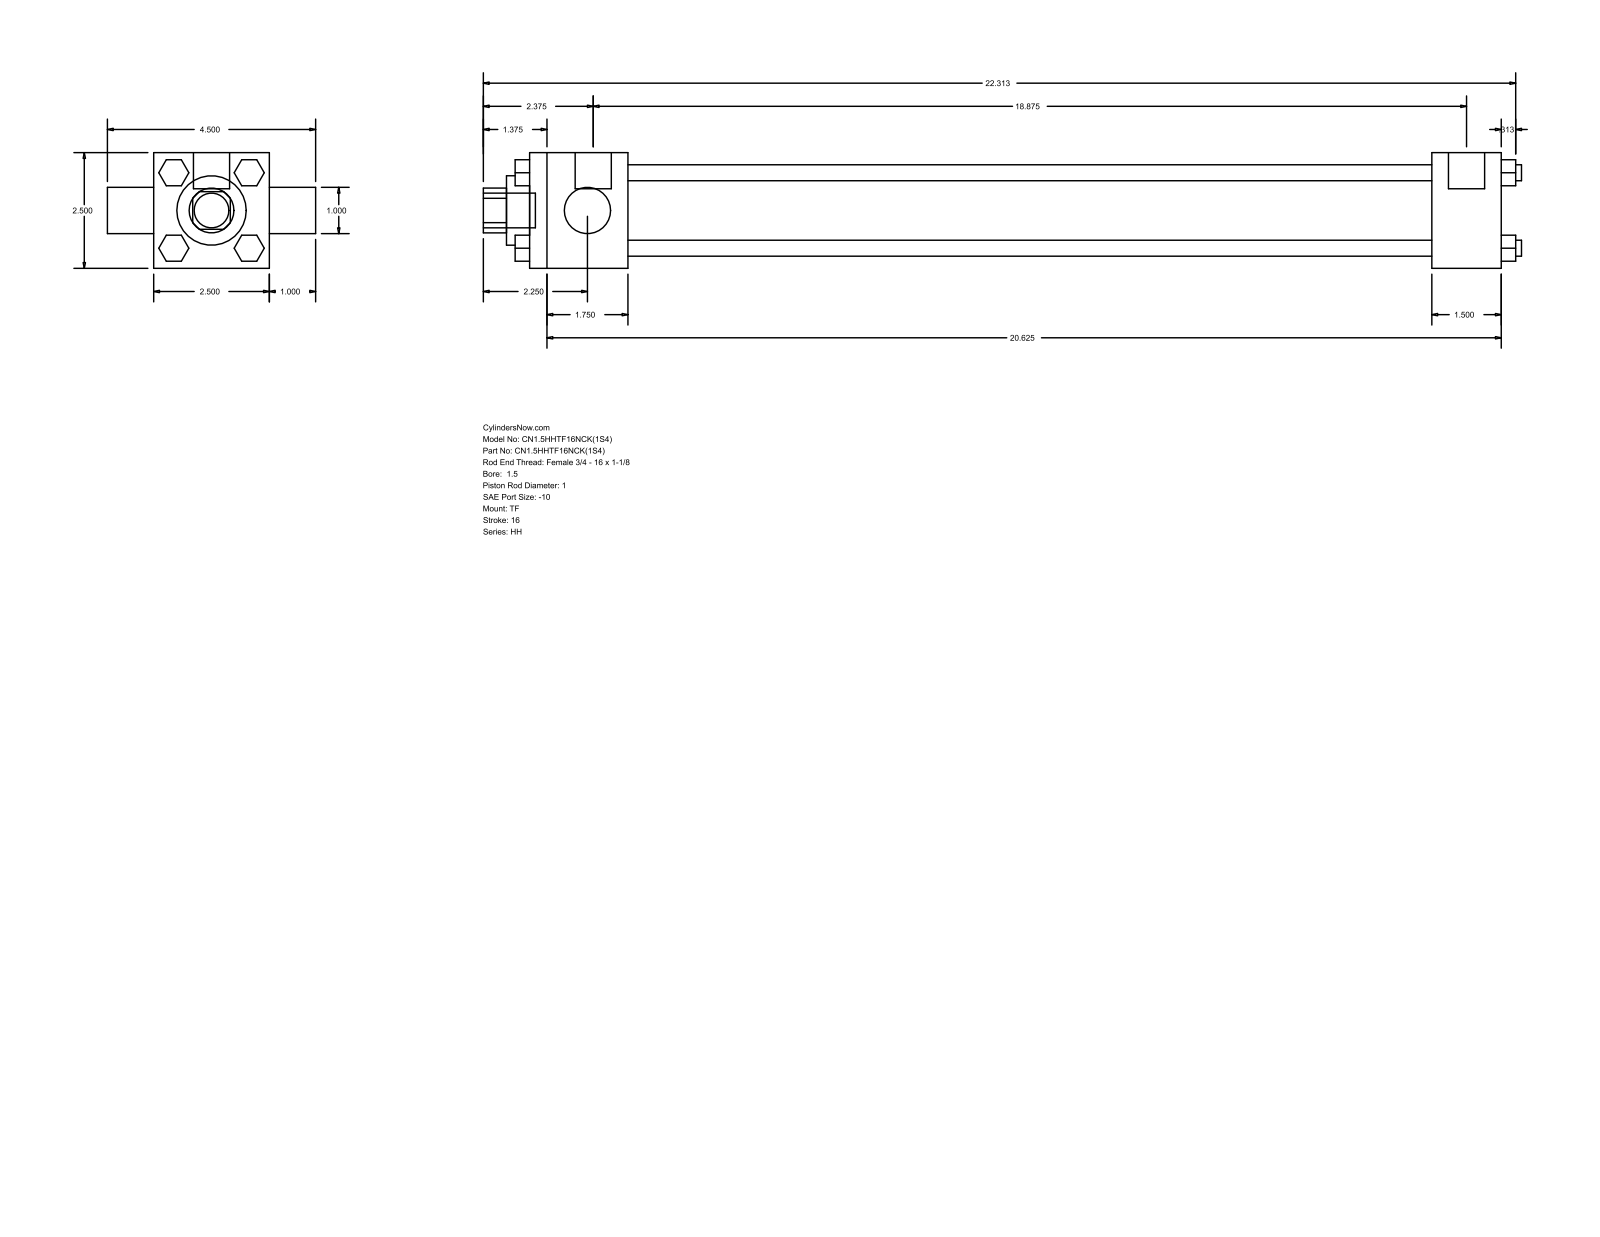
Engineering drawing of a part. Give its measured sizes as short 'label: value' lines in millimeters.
name: HH_TF__0150_1
written by: GSSL Pune (CONFIG_CONTROL_DESIGN)
unit: mm
bodies: 0 solids, 120 faces (92 planar, 28 cylindrical, 0 other)
size: 569.91 × 114.3 × 63.5
holes: 2× ⌀25.4, 1× ⌀38.1, 1× ⌀44.45
bosses: 4× ⌀8.76, 3× ⌀5.56, 2× ⌀19.84, 1× ⌀19.05
rounds: 1× R12.29
face distances: 63.5, 479.42, 441.32, 38.1, 53.98, 495.3, 533.4, 541.34, 25.4, 20.7
